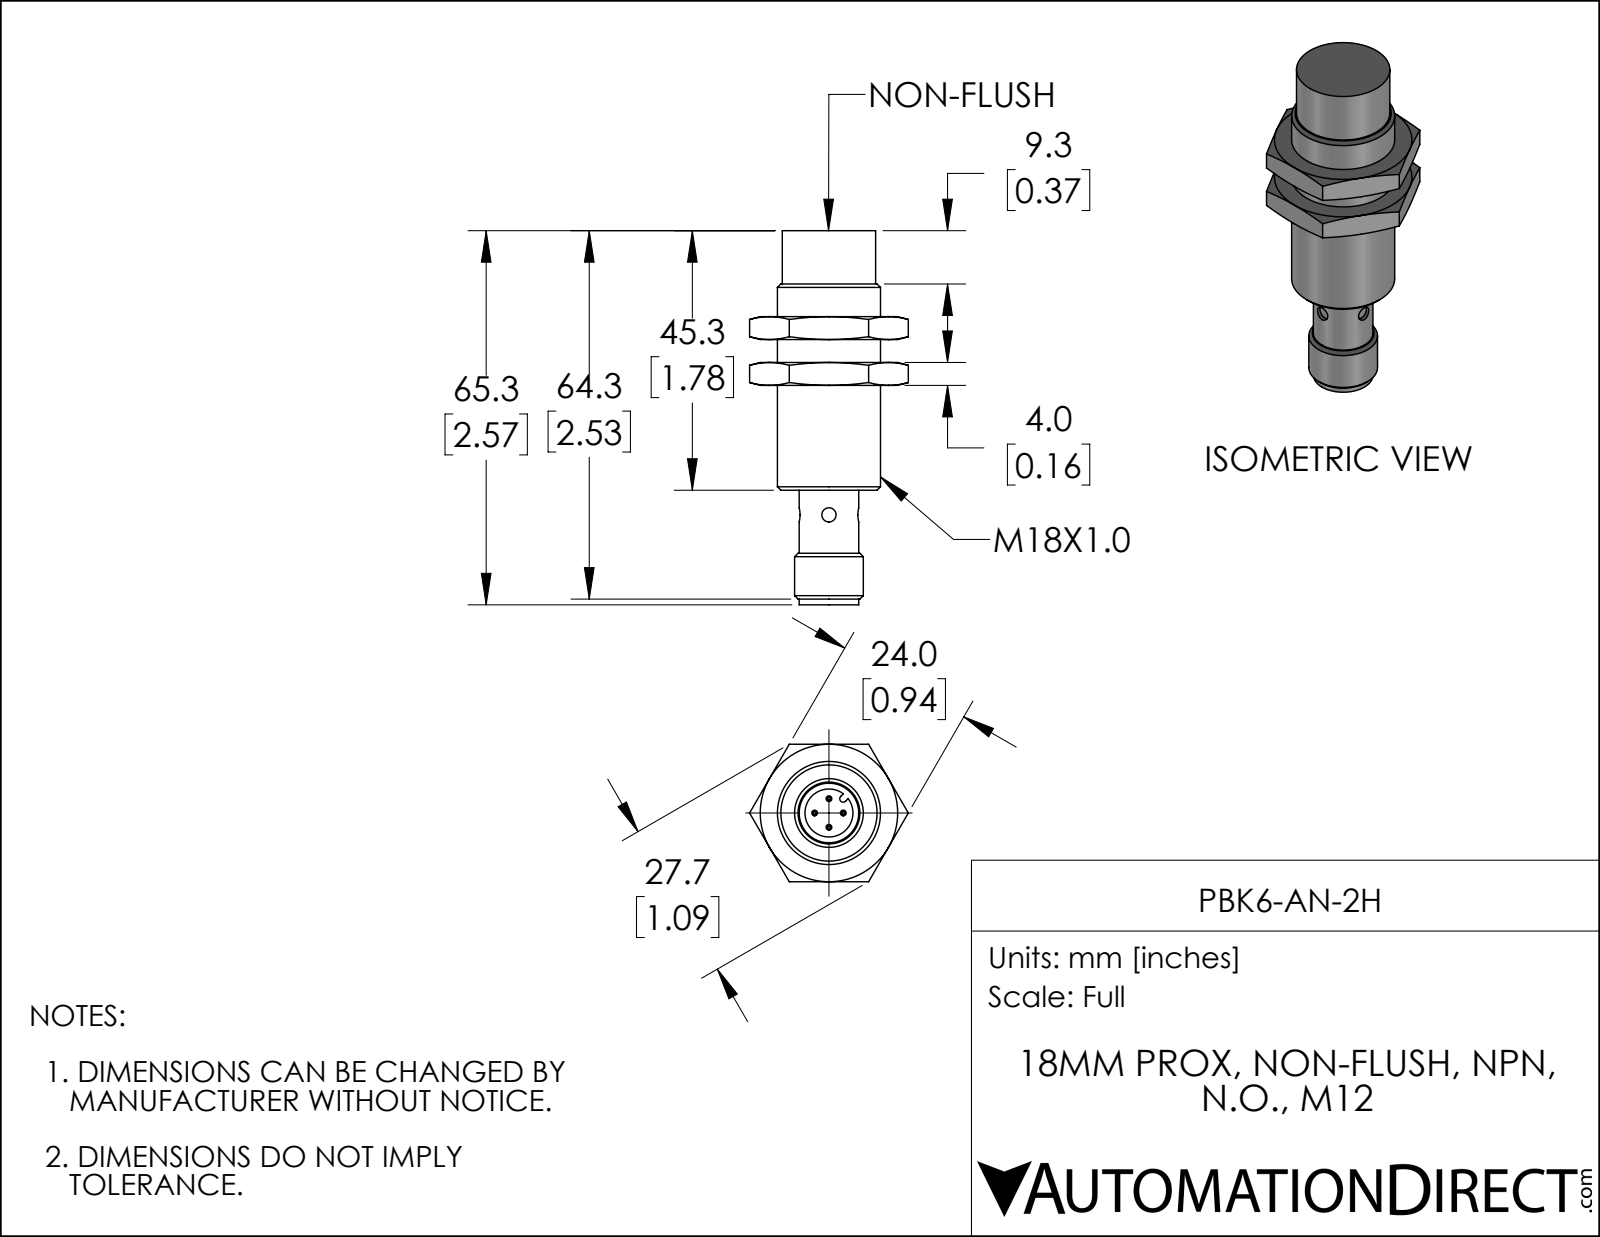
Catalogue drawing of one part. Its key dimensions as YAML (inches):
part_name: "DSD-0327"
step_written_by: "SolidWorks 2019 (AUTOMOTIVE_DESIGN)"
units: inches
bodies: {solids: 1, faces: 40, planar: 17, cylindrical: 15, other: 8}
overall_size: [2.571, 0.709, 0.709]
volume: 0.764
surface_area: 6.303
round_holes:
  - {diameter: 0.098, count: 2}
  - {diameter: 0.33, count: 1}
round_bosses_or_shafts:
  - {diameter: 0.039, count: 4}
  - {diameter: 0.709, count: 1}
  - {diameter: 0.642, count: 1}
  - {diameter: 0.472, count: 1}
  - {diameter: 0.409, count: 1}
partial_cylinders:
  - {radius: 0.024, count: 1}
face_to_face_distances: [1.783, 2.22, 0.437, 2.571, 0.787, 0.35, 0.354, 0.366, 1.417, 1.854]
